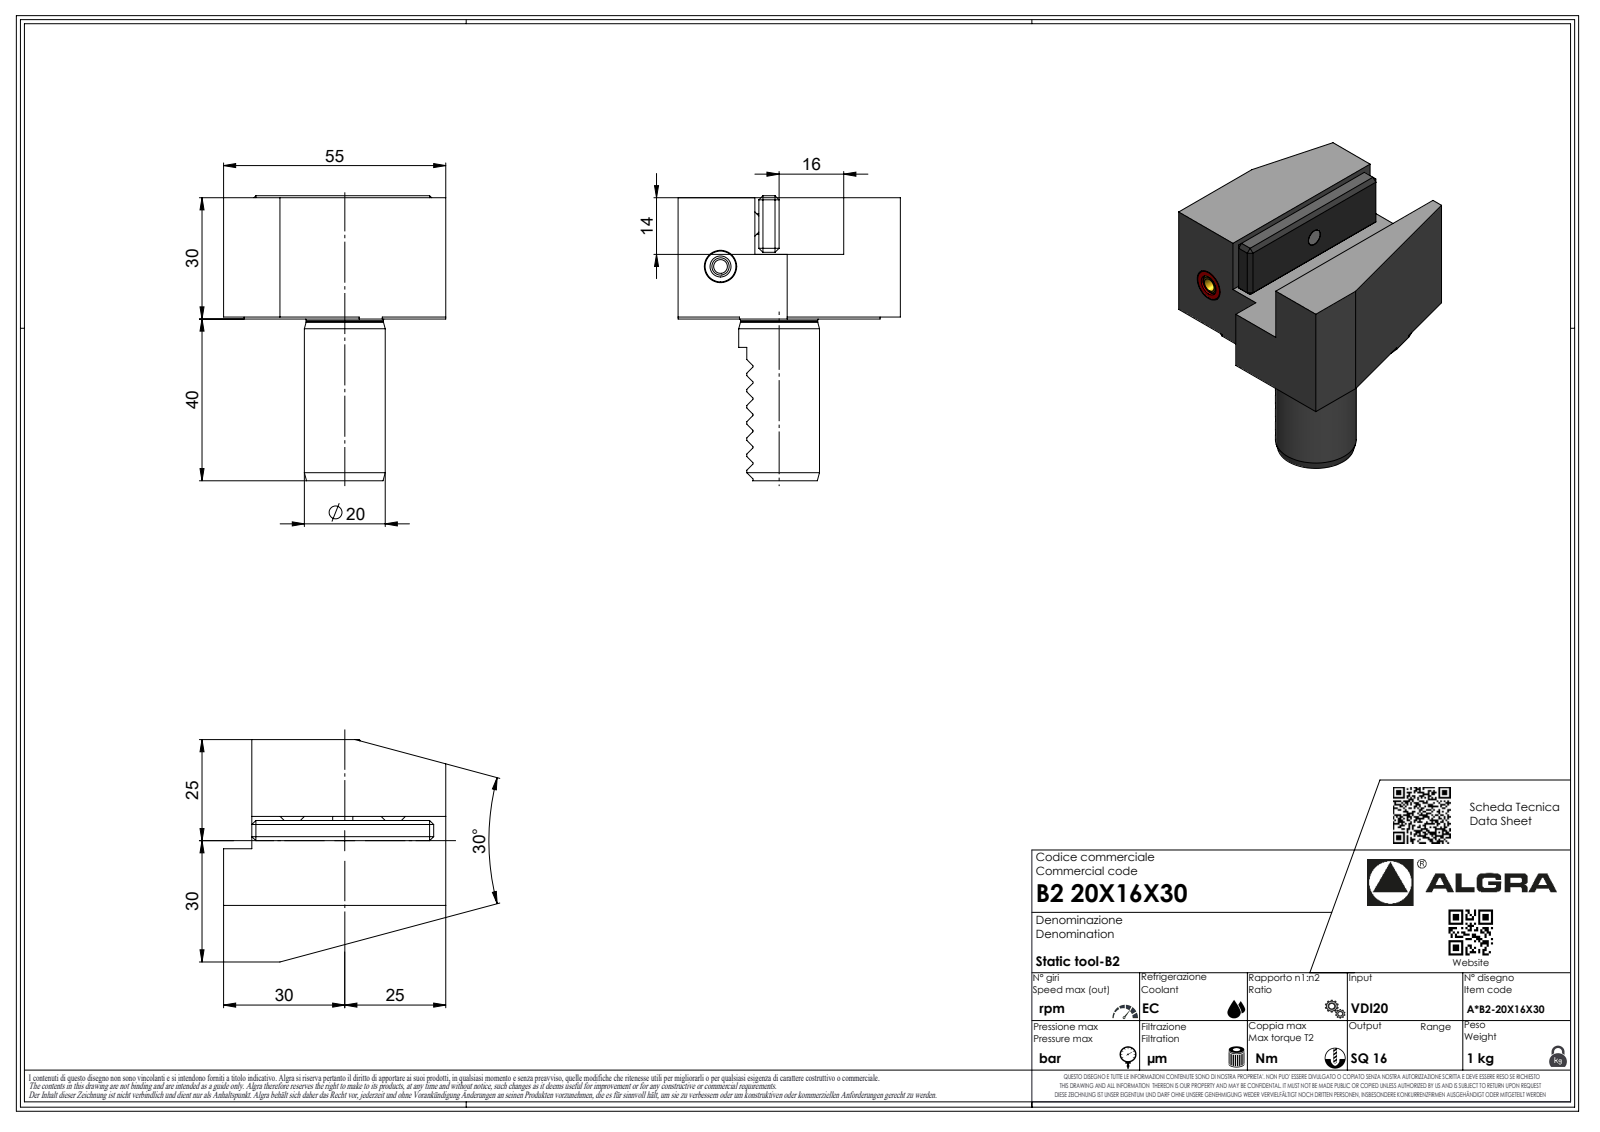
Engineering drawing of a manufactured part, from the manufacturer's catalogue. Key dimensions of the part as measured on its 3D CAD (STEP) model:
Part name (STEP PRODUCT): B220X16X30
STEP written by: SolidWorks 2023 (AUTOMOTIVE_DESIGN)
Units: millimetres
Bodies: 1 solid, 346 faces (235 planar, 39 cylindrical, 72 other)
Overall size (bounding box): 70.5 × 55 × 55
Volume: 74 983 mm³ · Surface area: 15 422 mm²
Round holes (diameter × count): ⌀2.1 ×1
Round bosses / shafts (diameter × count): ⌀50 ×1, ⌀20 ×1, ⌀19.1 ×1, ⌀6.37 ×1, ⌀1.7 ×1
Partial cylindrical surfaces — rounded edges, fillets, slot ends (radius × count): R0.3 ×8, R0.33 ×7, R0.52 ×7, R3.7 ×7, R0.21 ×1
Main face-to-face distances: 30, 14, 16, 55, 0.5, 41, 48, 7, 29.5, 15.5
